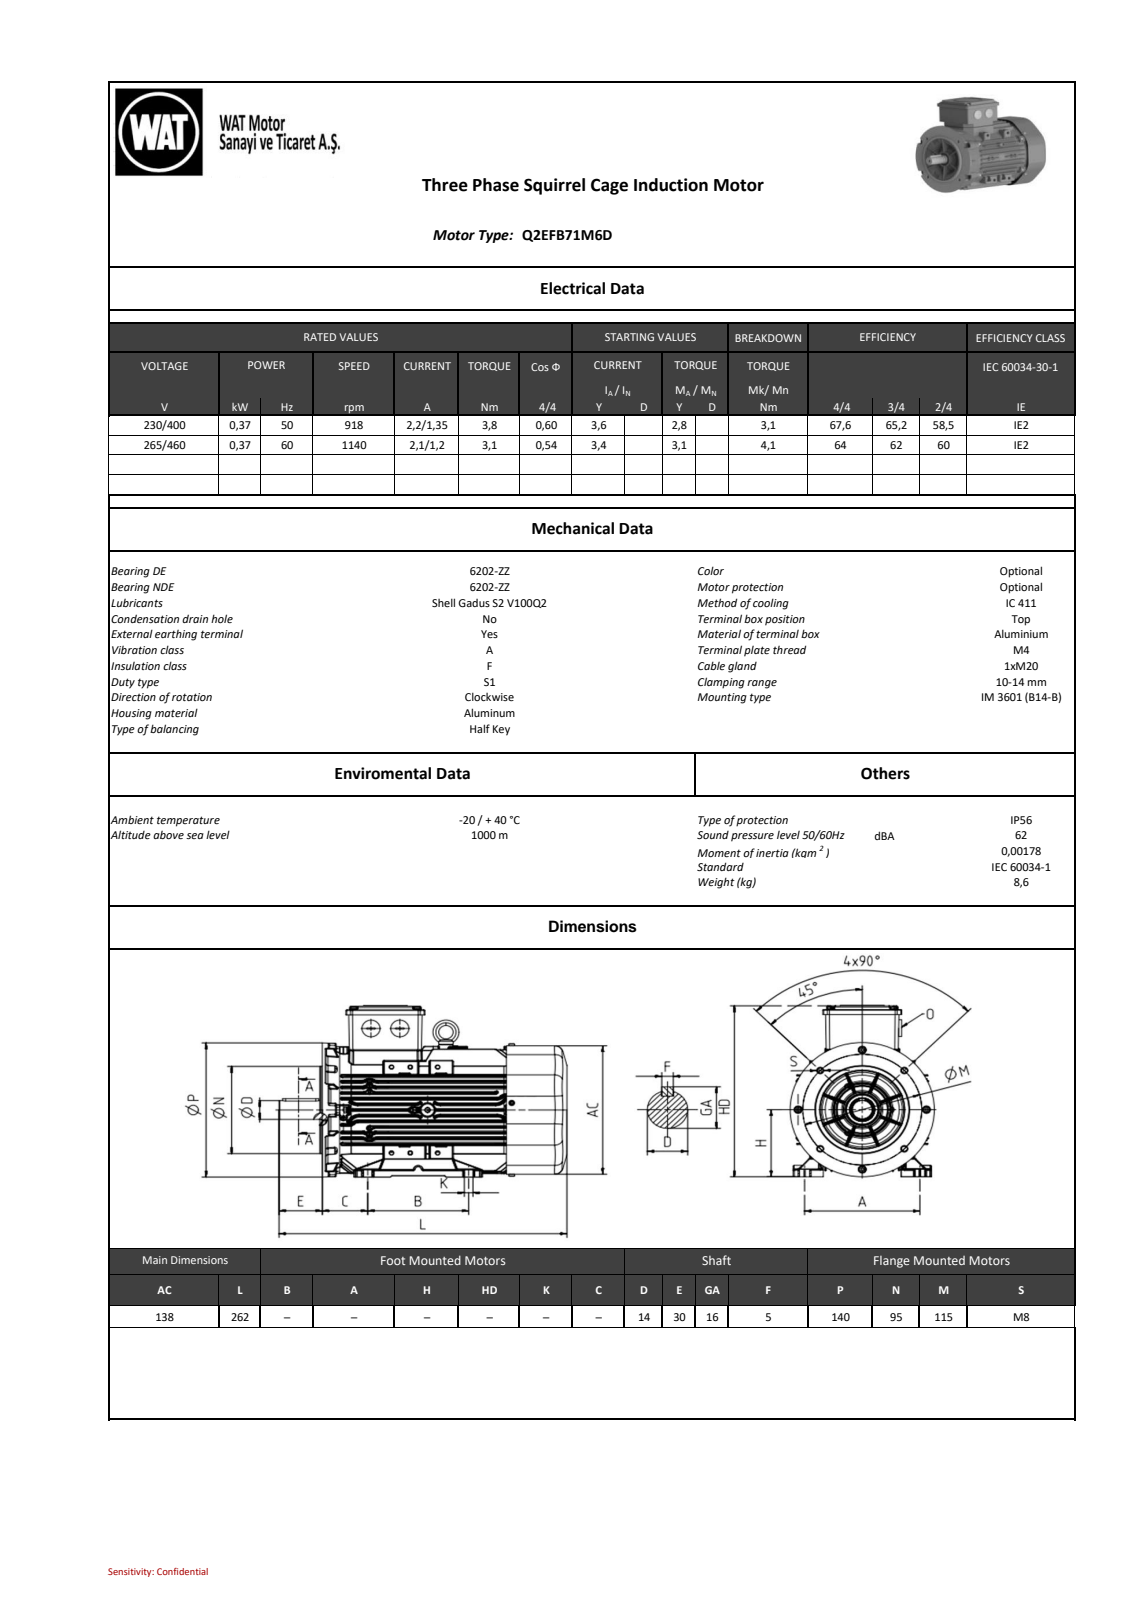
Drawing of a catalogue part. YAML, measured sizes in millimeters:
part_name: "001_objects"
step_written_by: "SIEMENS PLM Software NX2206.8101 (AUTOMOTIVE_DESIGN)"
units: millimeters
bodies: {solids: 0, faces: 2709, planar: 1361, cylindrical: 697, other: 651}
overall_size: [262, 177.35, 140.48]
round_holes:
  - {diameter: 3.65, count: 8}
  - {diameter: 4, count: 8}
  - {diameter: 2.5, count: 6}
  - {diameter: 3.3, count: 5}
  - {diameter: 5, count: 5}
  - {diameter: 8, count: 5}
  - {diameter: 4.5, count: 4}
  - {diameter: 4.65, count: 4}
  - {diameter: 4.8, count: 4}
  - {diameter: 3, count: 3}
  - {diameter: 3.7, count: 3}
  - {diameter: 4.6, count: 2}
round_bosses_or_shafts:
  - {diameter: 8, count: 8}
  - {diameter: 4, count: 8}
  - {diameter: 3.3, count: 4}
  - {diameter: 140.48, count: 1}
  - {diameter: 138, count: 1}
  - {diameter: 115, count: 1}
  - {diameter: 95, count: 1}
  - {diameter: 61, count: 1}
partial_cylinders:
  - {radius: 1, count: 79}
  - {radius: 0.5, count: 48}
  - {radius: 2, count: 37}
  - {radius: 1.2, count: 36}
  - {radius: 1.5, count: 24}
  - {radius: 4, count: 17}
  - {radius: 5, count: 17}
  - {radius: 10, count: 16}
face_to_face_distances: [2, 3, 197.5, 194.5, 83, 1, 35, 6.9, 5, 1.5]
hole_center_spacings: [61.39, 84.39, 84.47, 87.43, 55, 36.59, 67.18, 67.2]
